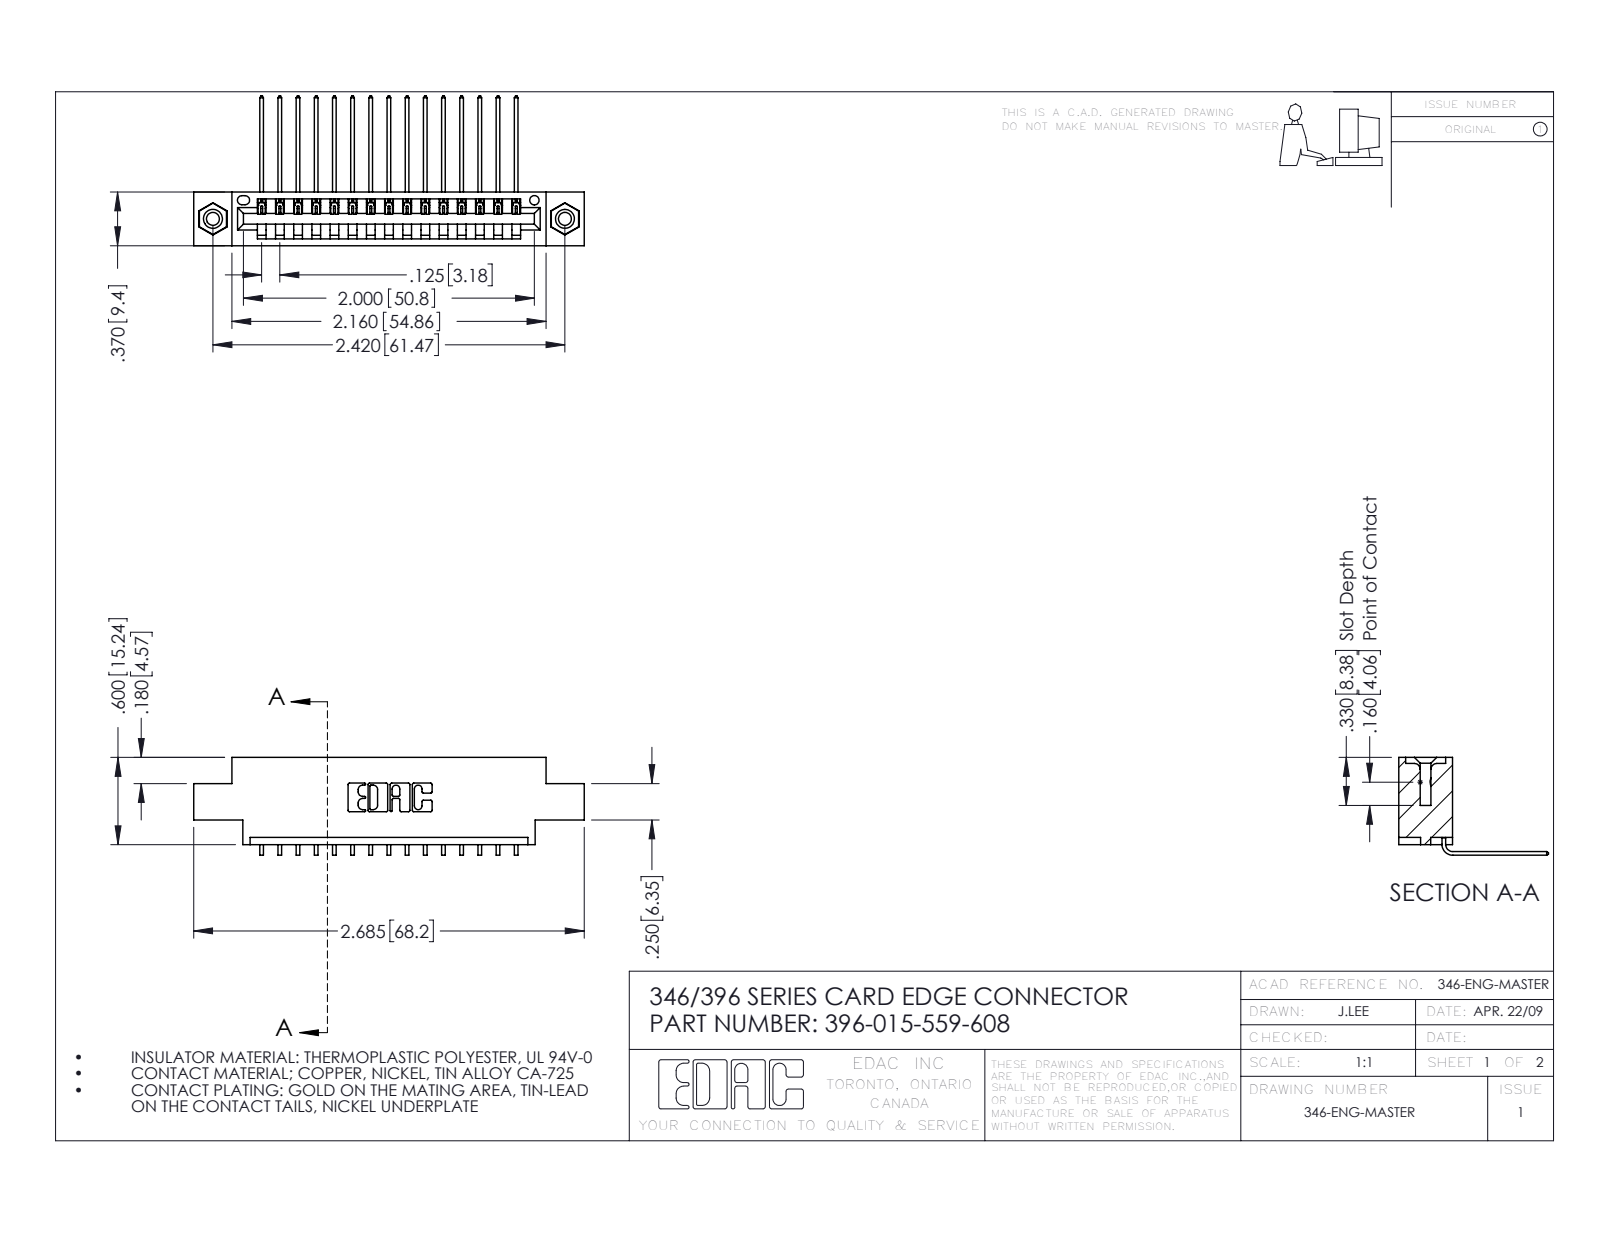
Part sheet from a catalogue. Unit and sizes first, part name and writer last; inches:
Units: inches
Overall size (bounding box): 2.685 × 1.03 × 0.673
Round holes (diameter × count): ⌀0.089 ×2, ⌀0.125 ×2, ⌀0.156 ×2, ⌀0.064 ×1
Round bosses / shafts (diameter × count): ⌀0.155 ×2
Partial cylindrical surfaces — rounded edges, fillets, slot ends (radius × count): R0.006 ×30, R0.01 ×22, R0.007 ×6, R0.031 ×6, R0.026 ×3, R0.031 ×2, R0.04 ×2, R0.014 ×1
Main face-to-face distances: 0.048, 0.37, 0.322, 0.25, 0.025, 0.072, 0.222, 0.148, 0.1, 0.174
Hole centre spacings: 0.246, 2.213, 2.42
Volume: 0.38 in³ · Surface area: 12.36 in²
Bodies: 18 solids, 1086 faces (742 planar, 328 cylindrical, 16 other)
Part name (STEP PRODUCT): 346 Part_0.170 Offset - 0.156 Dia-TI; 396-015-559-608; 345-292-001_558 559 Tail - 1; 345-250-001_345-250-003-102
STEP written by: SolidWorks 2016 (CONFIG_CONTROL_DESIGN)
